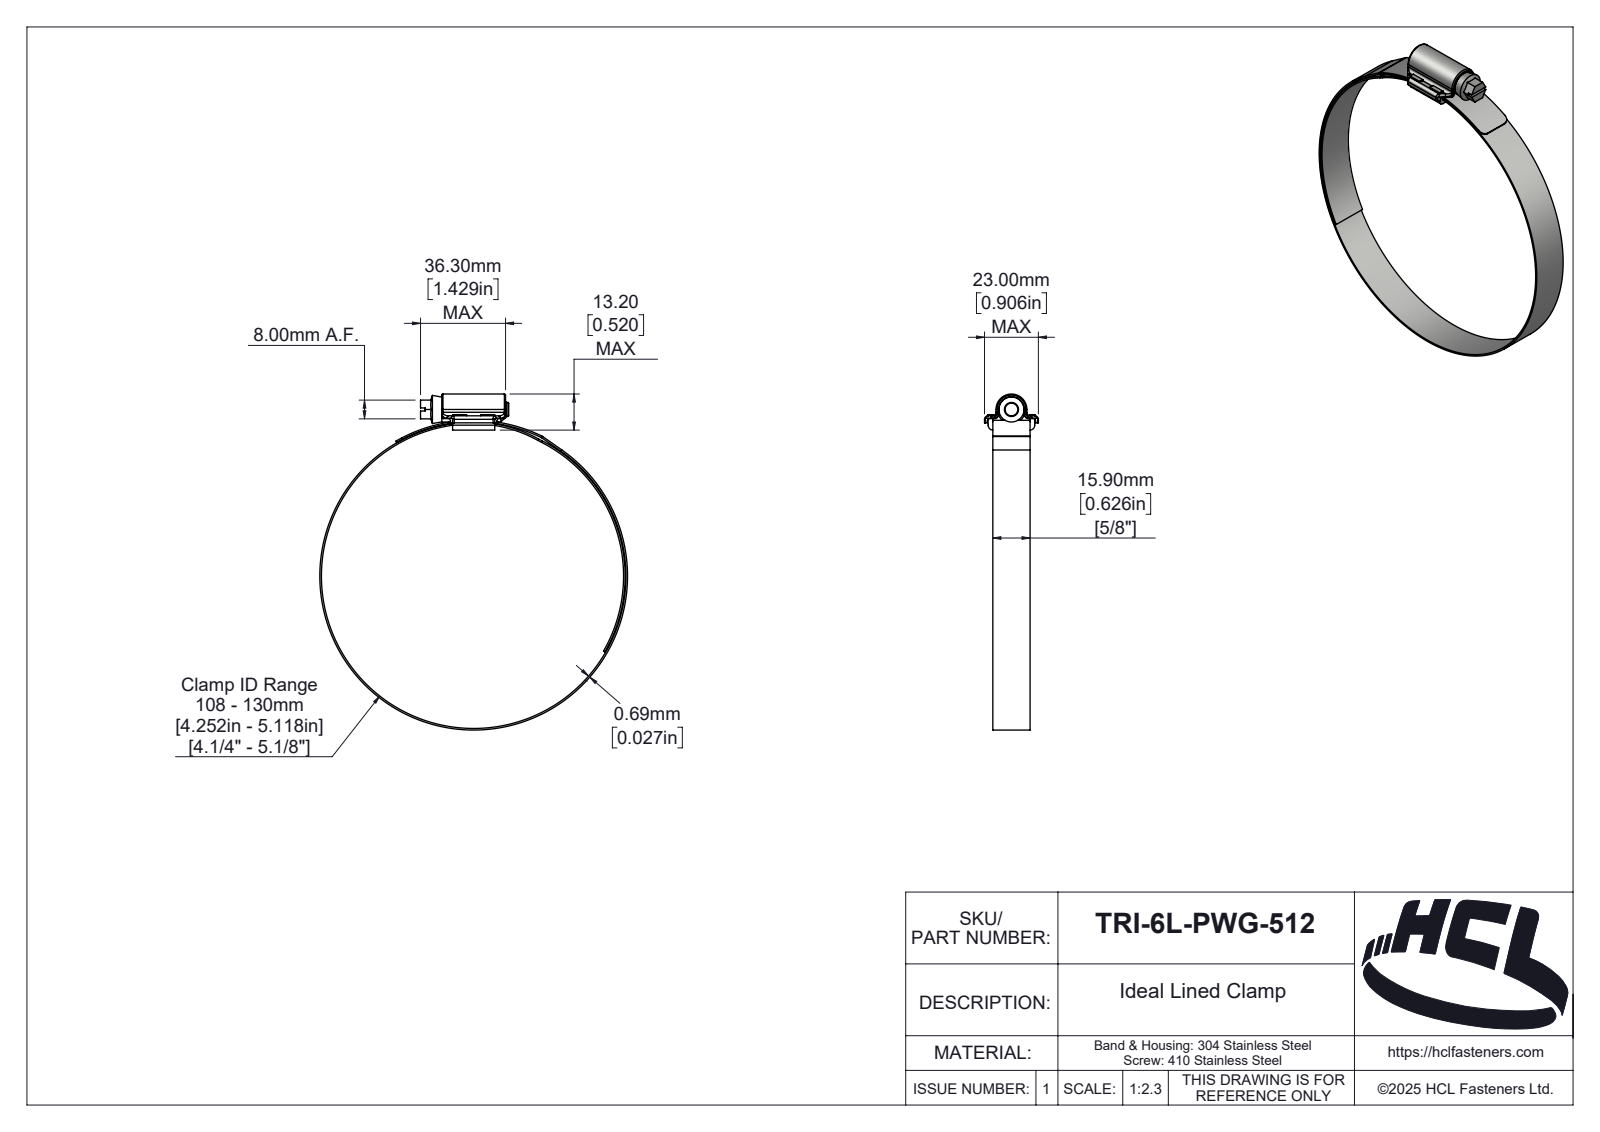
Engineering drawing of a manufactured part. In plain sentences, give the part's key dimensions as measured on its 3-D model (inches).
The part is named "TRI-6L-PWG-512". Its 3-D file was written by "SolidWorks 2025 (AUTOMOTIVE_DESIGN)". It is 4 solids with 268 faces: 87 planar, 102 cylindrical and 79 other. Overall it measures 5.645 by 5.172 by 0.906 inches. Its volume is 0.706 cubic inches and its surface area 37 square inches. Round holes: 1 of diameter 5.118. Round bosses or shafts: 1 of diameter 5.172, 1 of diameter 0.421, 1 of diameter 0.236. Partial cylindrical surfaces (rounded edges, fillets, slot ends): 14 of radius 0.039, 4 of radius 0.02, 4 of radius 0.059, 3 of radius 0.079, 2 of radius 0.004, 2 of radius 0.083, 2 of radius 0.118, 1 of radius 0.018. The main face-to-face distances are 0.626, 0.079, 0.705, 0.193, 0.027, 0.047, 0.179, 0.132, 0.604, 0.1.
